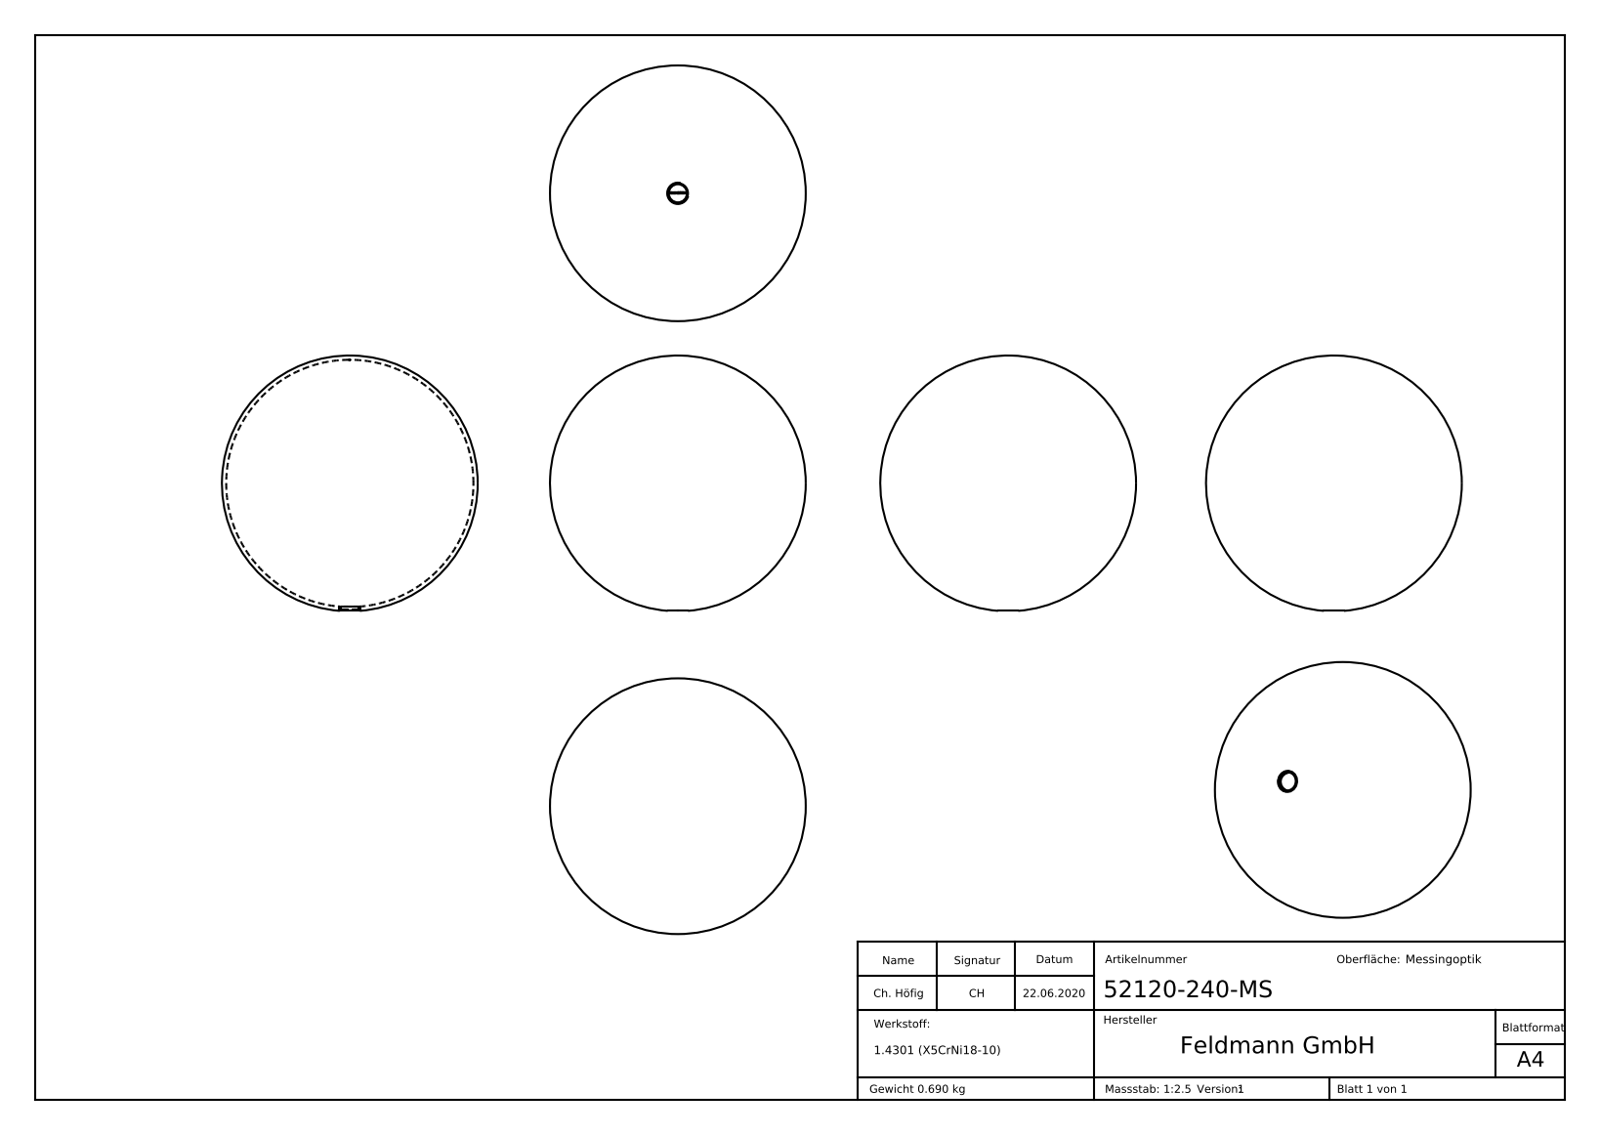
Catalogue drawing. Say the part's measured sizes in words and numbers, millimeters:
The part is named "52120-240-MS". Its 3-D file was written by "SolidWorks 2015 (CONFIG_CONTROL_DESIGN)". It is 1 solid with 257 faces: 120 planar, 1 cylindrical and 136 other. Overall it measures 120 by 120 by 119.81 millimeters. Its volume is 87 378 cubic millimeters and its surface area 87 448 square millimeters. Round holes: 1 of diameter 8.5. The main face-to-face distances are 0.45, 1.12, 0.5, 0.76, 0.52, 0.33, 1.85, 3.2, 0.62, 1.93.
